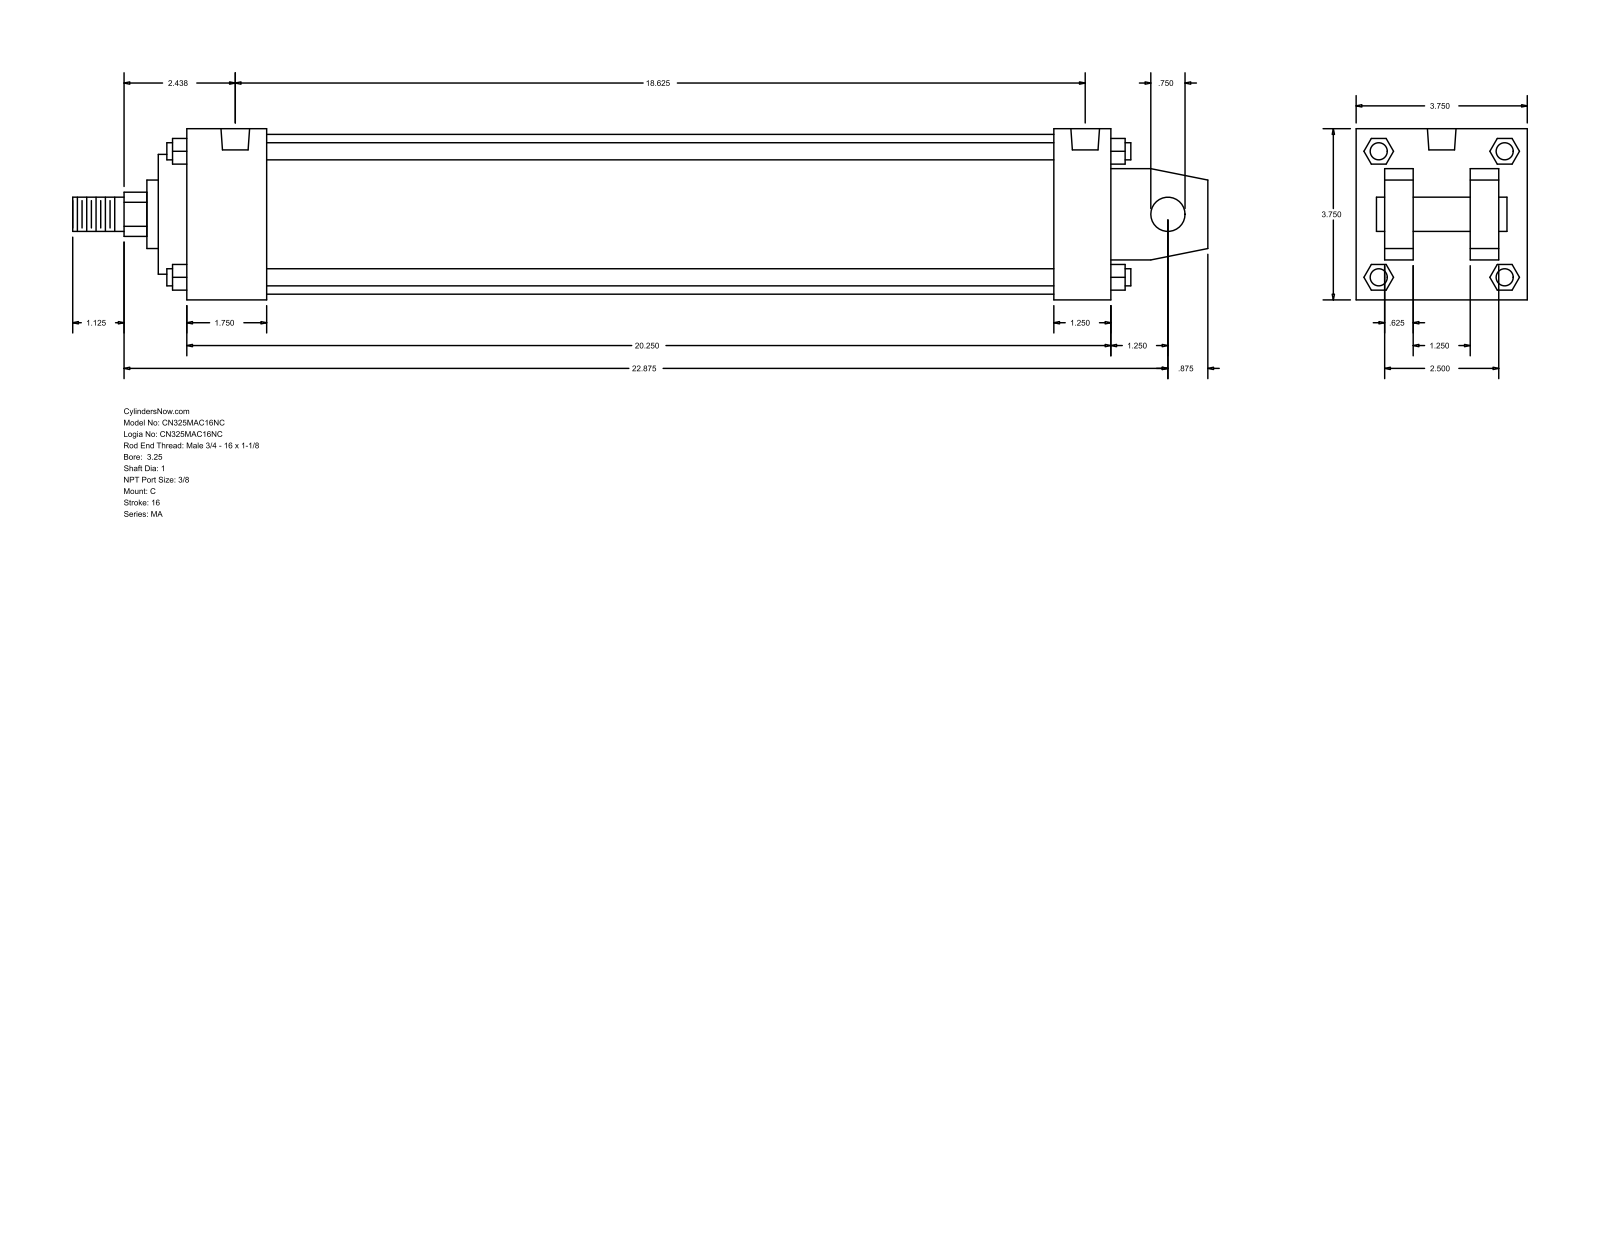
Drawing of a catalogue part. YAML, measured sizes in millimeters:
part_name: "MA_C__0325_1"
step_written_by: "GSSL Pune (CONFIG_CONTROL_DESIGN)"
units: millimeters
bodies: {solids: 0, faces: 141, planar: 109, cylindrical: 32, other: 0}
overall_size: [631.83, 95.25, 95.25]
round_holes:
  - {diameter: 11.11, count: 4}
  - {diameter: 15.93, count: 2}
round_bosses_or_shafts:
  - {diameter: 9.53, count: 4}
  - {diameter: 19.05, count: 2}
  - {diameter: 88.9, count: 1}
  - {diameter: 66.67, count: 1}
  - {diameter: 38.1, count: 1}
  - {diameter: 25.4, count: 1}
partial_cylinders:
  - {radius: 12.29, count: 1}
face_to_face_distances: [95.24, 15.87, 63.5, 514.35, 31.74, 79.37, 47.63, 530.22, 482.6, 31.75]
hole_center_spacings: [4.76, 463.56, 468.32, 473.08]
